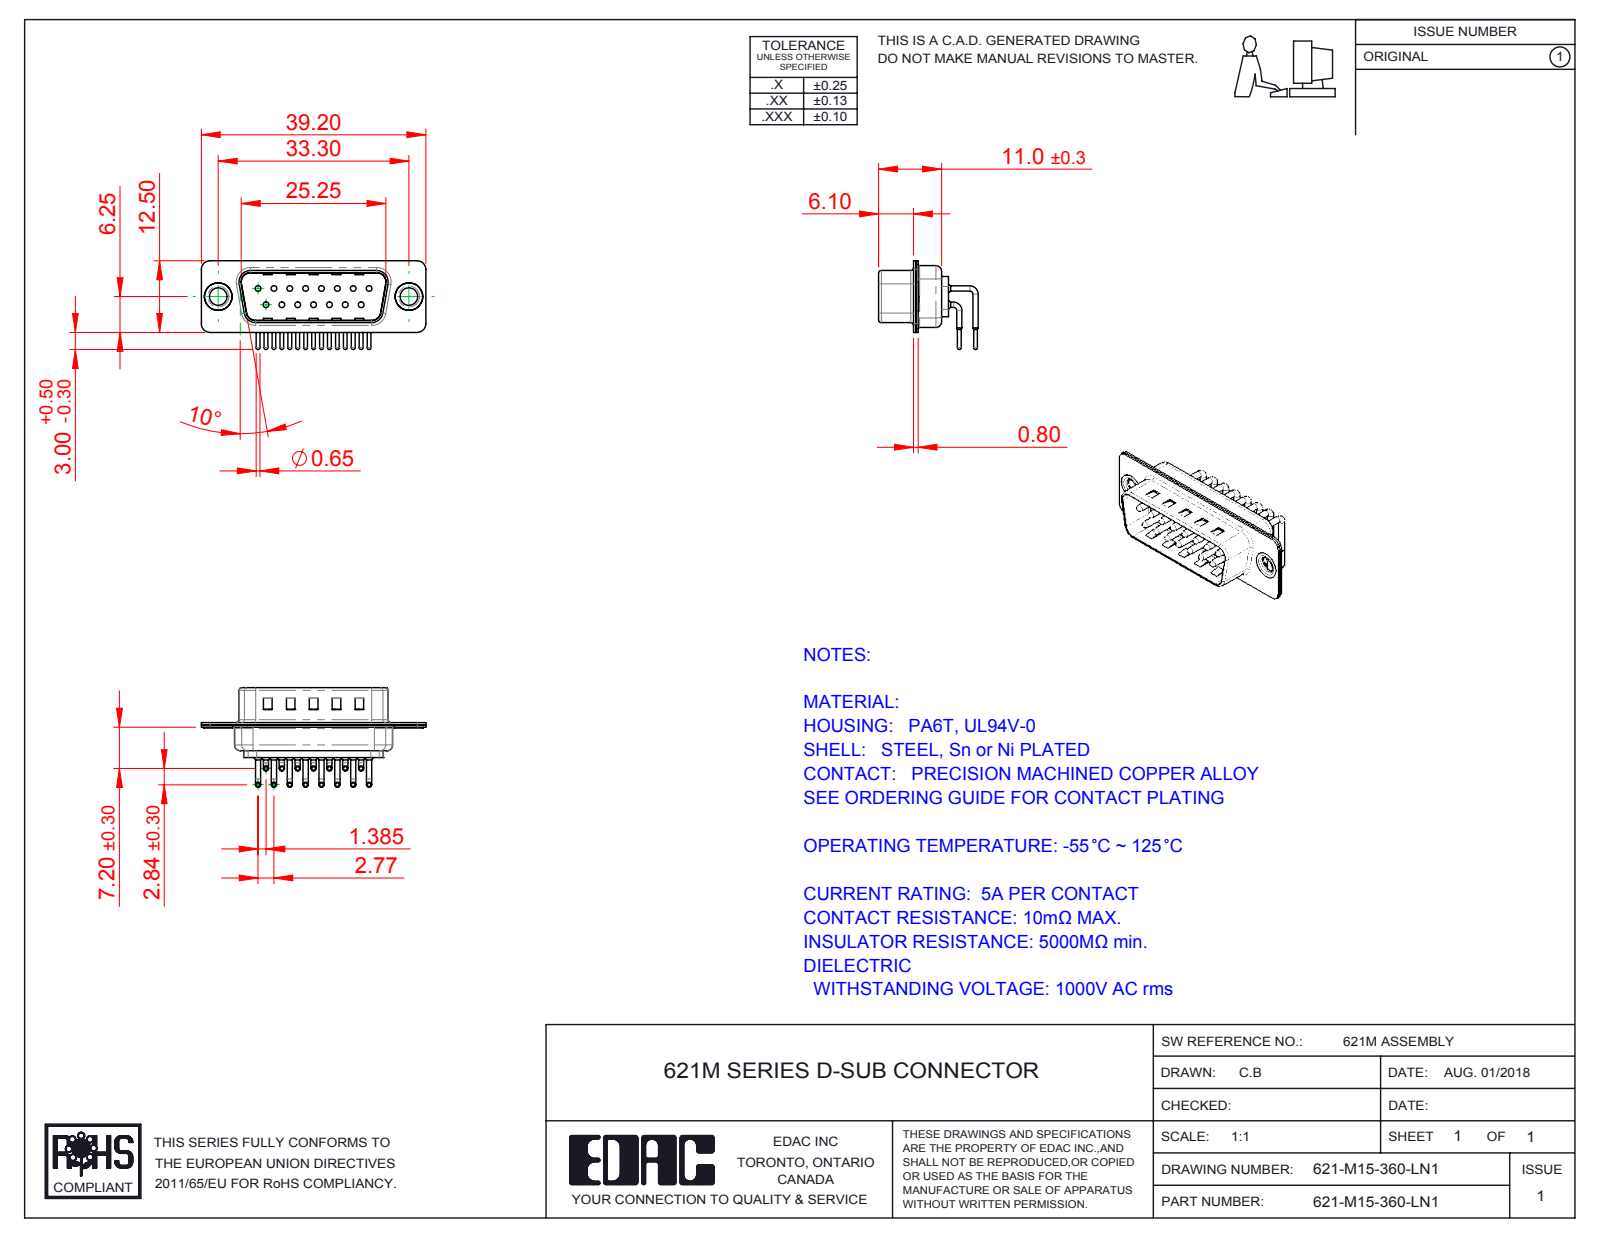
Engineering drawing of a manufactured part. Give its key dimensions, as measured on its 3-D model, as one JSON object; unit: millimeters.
{"part_name": "621M Contact Row 1; 621M Housing_15 Contacts; 621M Contact Row 2; 621M Shell Front_15 Contacts (+3 more)", "step_written_by": "SolidWorks 2016 (CONFIG_CONTROL_DESIGN)", "units": "millimeters", "bodies": {"solids": 20, "faces": 1964, "planar": 1099, "cylindrical": 657, "other": 208}, "overall_size": [39.2, 17.39, 15.49], "volume_mm3": 1859, "surface_area_mm2": 5111, "round_holes": [[1, 15], [1.7, 15], [2, 15], [3.05, 2], [4, 2], [4.8, 2]], "round_bosses_or_shafts": [[0.9, 30], [1.5, 15], [0.65, 15], [5, 2], [4.9, 2], [3.55, 2]], "partial_cylinders_radius": [[1.5, 16], [1.01, 15], [2, 12], [0.5, 8], [1.6, 8], [0.25, 4], [0.6, 4], [0.65, 4]], "face_to_face_distances": [0.4, 0.85, 9.55, 8.7, 1.25, 0.8, 10.4, 1.5, 0.35, 1.9], "hole_center_spacings": [3.16, 2.77, 5.54, 8.31, 11.08, 5.03, 5.04, 7.48]}
